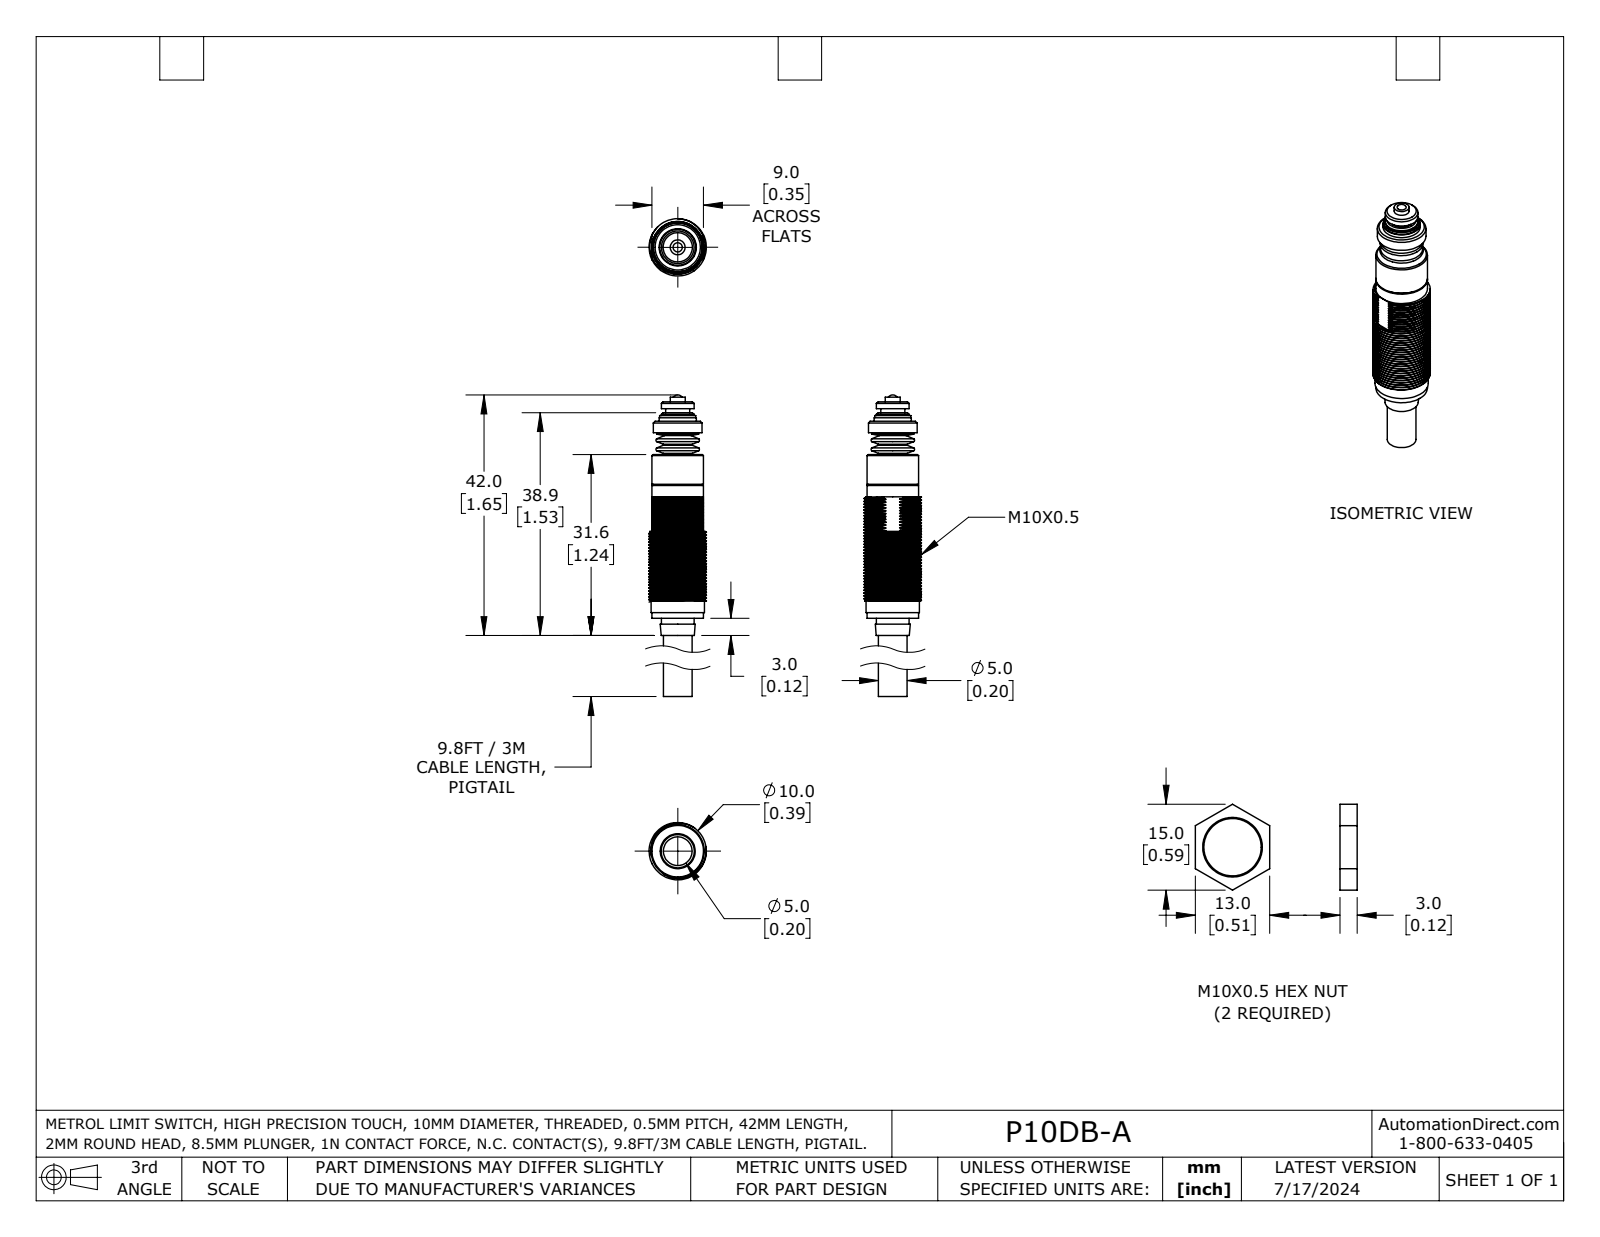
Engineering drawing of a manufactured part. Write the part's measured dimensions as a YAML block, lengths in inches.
part_name: "P10DB-A"
step_written_by: "SolidWorks 2023 (CONFIG_CONTROL_DESIGN)"
units: inches
bodies: {solids: 2, faces: 180, planar: 25, cylindrical: 64, other: 91}
overall_size: [1.969, 0.394, 0.394]
volume: 0.158
surface_area: 3.066
round_bosses_or_shafts:
  - {diameter: 0.394, count: 1}
  - {diameter: 0.366, count: 1}
  - {diameter: 0.354, count: 1}
  - {diameter: 0.335, count: 1}
  - {diameter: 0.287, count: 1}
  - {diameter: 0.256, count: 1}
  - {diameter: 0.248, count: 1}
  - {diameter: 0.224, count: 1}
face_to_face_distances: [1.413, 1.126, 0.287, 0.079, 1.559, 0.354, 1.354, 0.433, 0.362, 0.213]
